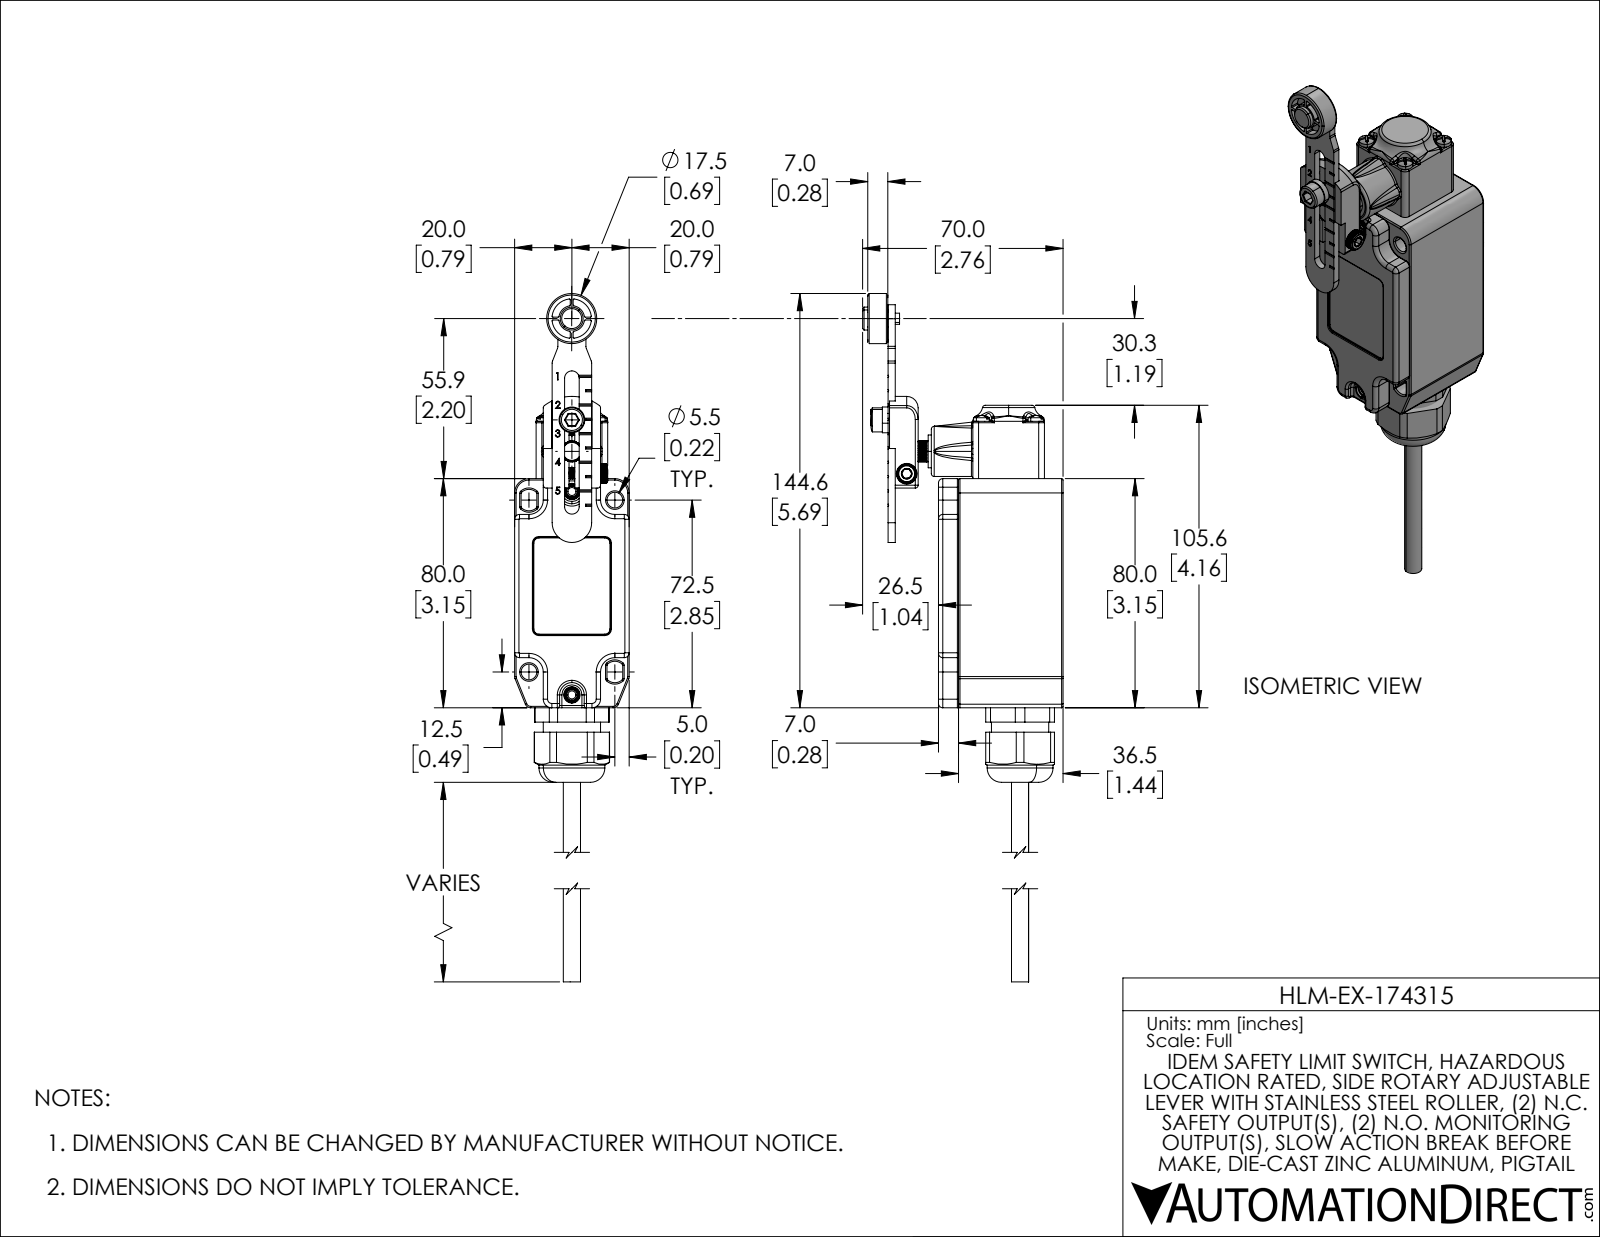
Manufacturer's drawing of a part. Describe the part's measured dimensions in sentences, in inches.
The part is named "HLM-EX-174315". Its 3-D file was written by "SolidWorks 2021 (AUTOMOTIVE_DESIGN)". It is 19 solids with 3507 faces: 1011 planar, 910 cylindrical and 1586 other. Overall it measures 9.001 by 2.756 by 1.575 inches. Its volume is 5.297 cubic inches and its surface area 95.15 square inches. Round holes: 10 of diameter 0.118, 4 of diameter 0.106, 4 of diameter 0.134, 3 of diameter 0.161, 2 of diameter 0.146, 2 of diameter 0.15, 2 of diameter 0.157, 2 of diameter 0.165, 2 of diameter 0.217, 2 of diameter 0.571, 1 of diameter 0.114, 1 of diameter 0.126. Round bosses or shafts: 6 of diameter 0.244, 4 of diameter 0.216, 3 of diameter 0.252, 2 of diameter 0.689, 2 of diameter 0.354, 2 of diameter 0.154, 1 of diameter 0.906, 1 of diameter 0.728. Partial cylindrical surfaces (rounded edges, fillets, slot ends): 162 of radius 0.02, 36 of radius 0.012, 26 of radius 0.016, 24 of radius 0.039, 16 of radius 0.079, 14 of radius 0.006, 10 of radius 0.031, 9 of radius 0.059. The main face-to-face distances are 0.089, 0.098, 1.486, 1.575, 2.307, 0.102, 1.398, 1.512, 0.276, 0.697. The hole center spacings are 0.748, 0.529, 1.258, 0.354, 0.432, 0.65, 0.75, 0.828.
